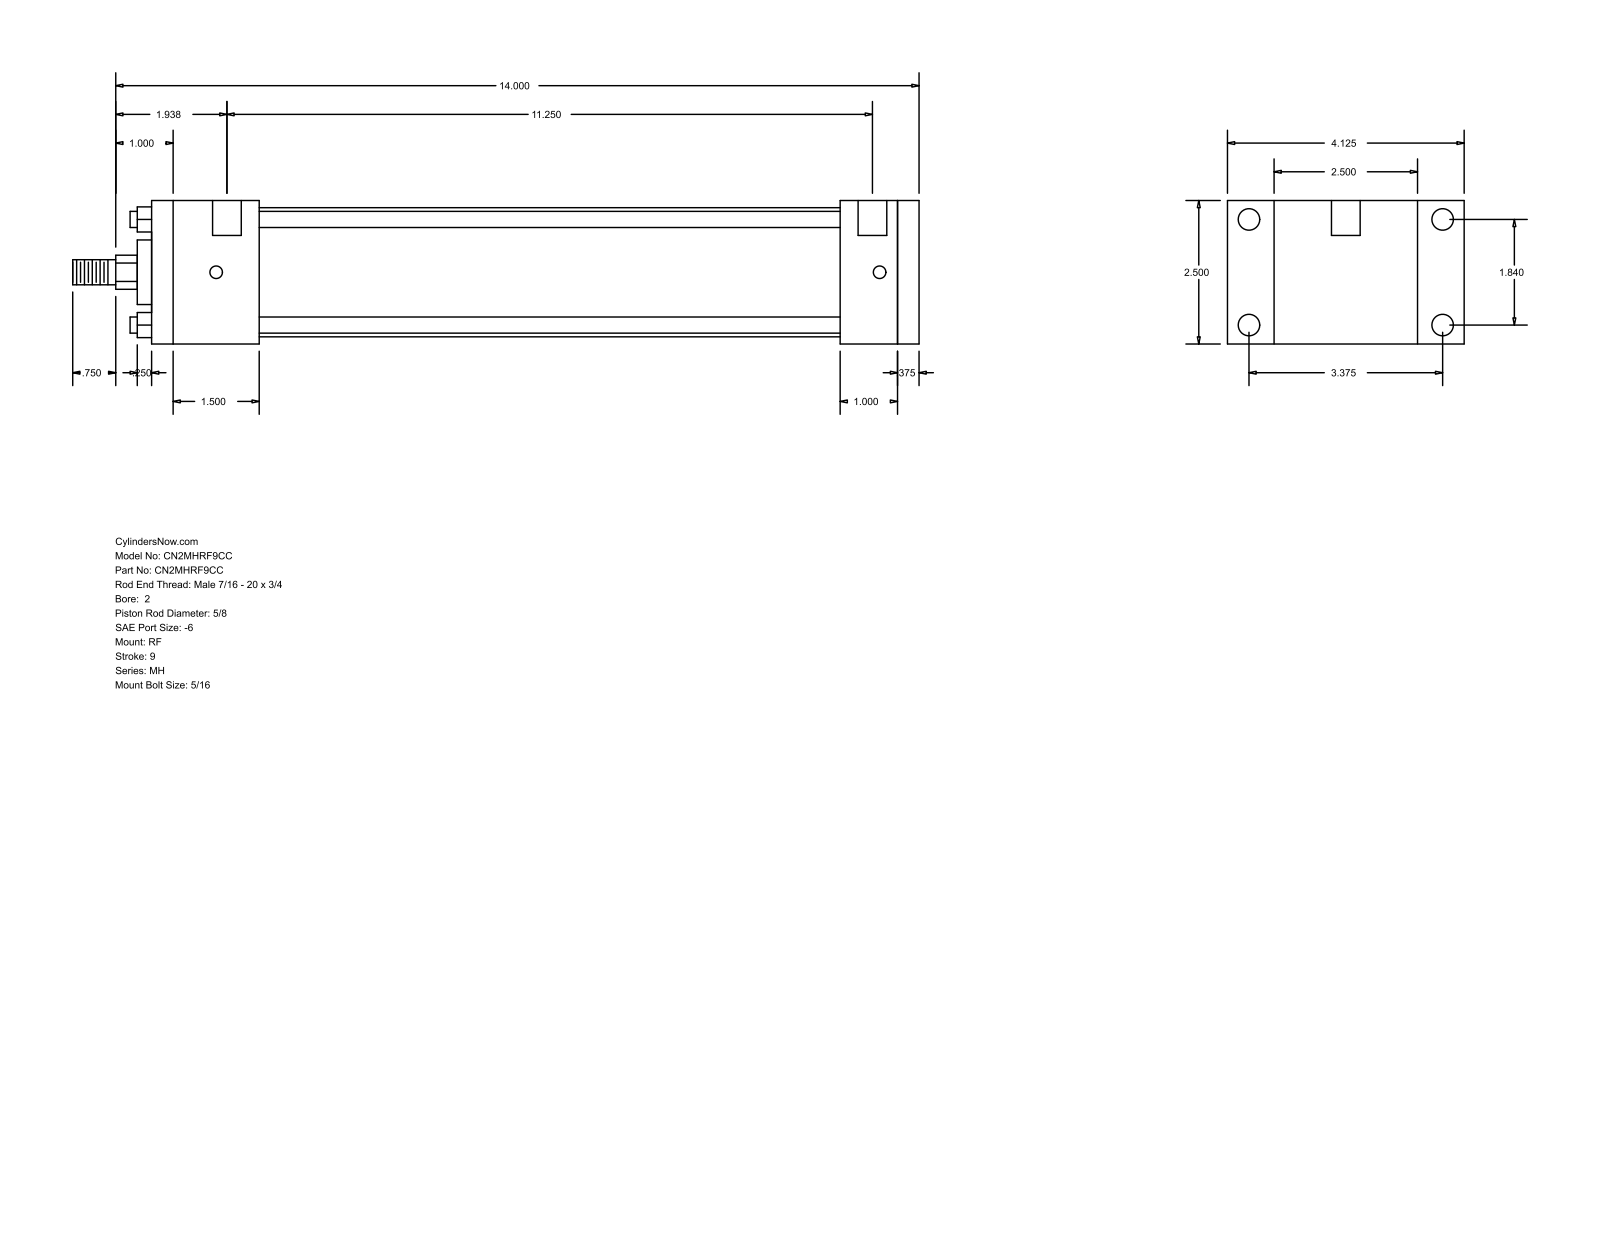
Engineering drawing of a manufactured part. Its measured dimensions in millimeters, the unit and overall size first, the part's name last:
Units: millimetres
Overall size (bounding box): 374.65 × 104.78 × 63.5
Round holes (diameter × count): ⌀5.56 ×4, ⌀9.53 ×4, ⌀12.7 ×2
Round bosses / shafts (diameter × count): ⌀7.14 ×4, ⌀57.15 ×1, ⌀28.57 ×1, ⌀15.88 ×1, ⌀11.11 ×1
Partial cylindrical surfaces — rounded edges, fillets, slot ends (radius × count): R7.54 ×1
Main face-to-face distances: 63.5, 339.72, 9.53, 330.19, 47.62, 304.8, 257.18, 282.57, 292.1, 25.39
Hole centre spacings: 46.74, 85.72, 97.63, 293.69, 3.18, 4.76, 285.75, 288.93
Bodies: 0 solids, 92 faces (64 planar, 28 cylindrical, 0 other)
Part name (STEP PRODUCT): MH_RF__0200_0.625
STEP written by: GSSL Pune (CONFIG_CONTROL_DESIGN)
